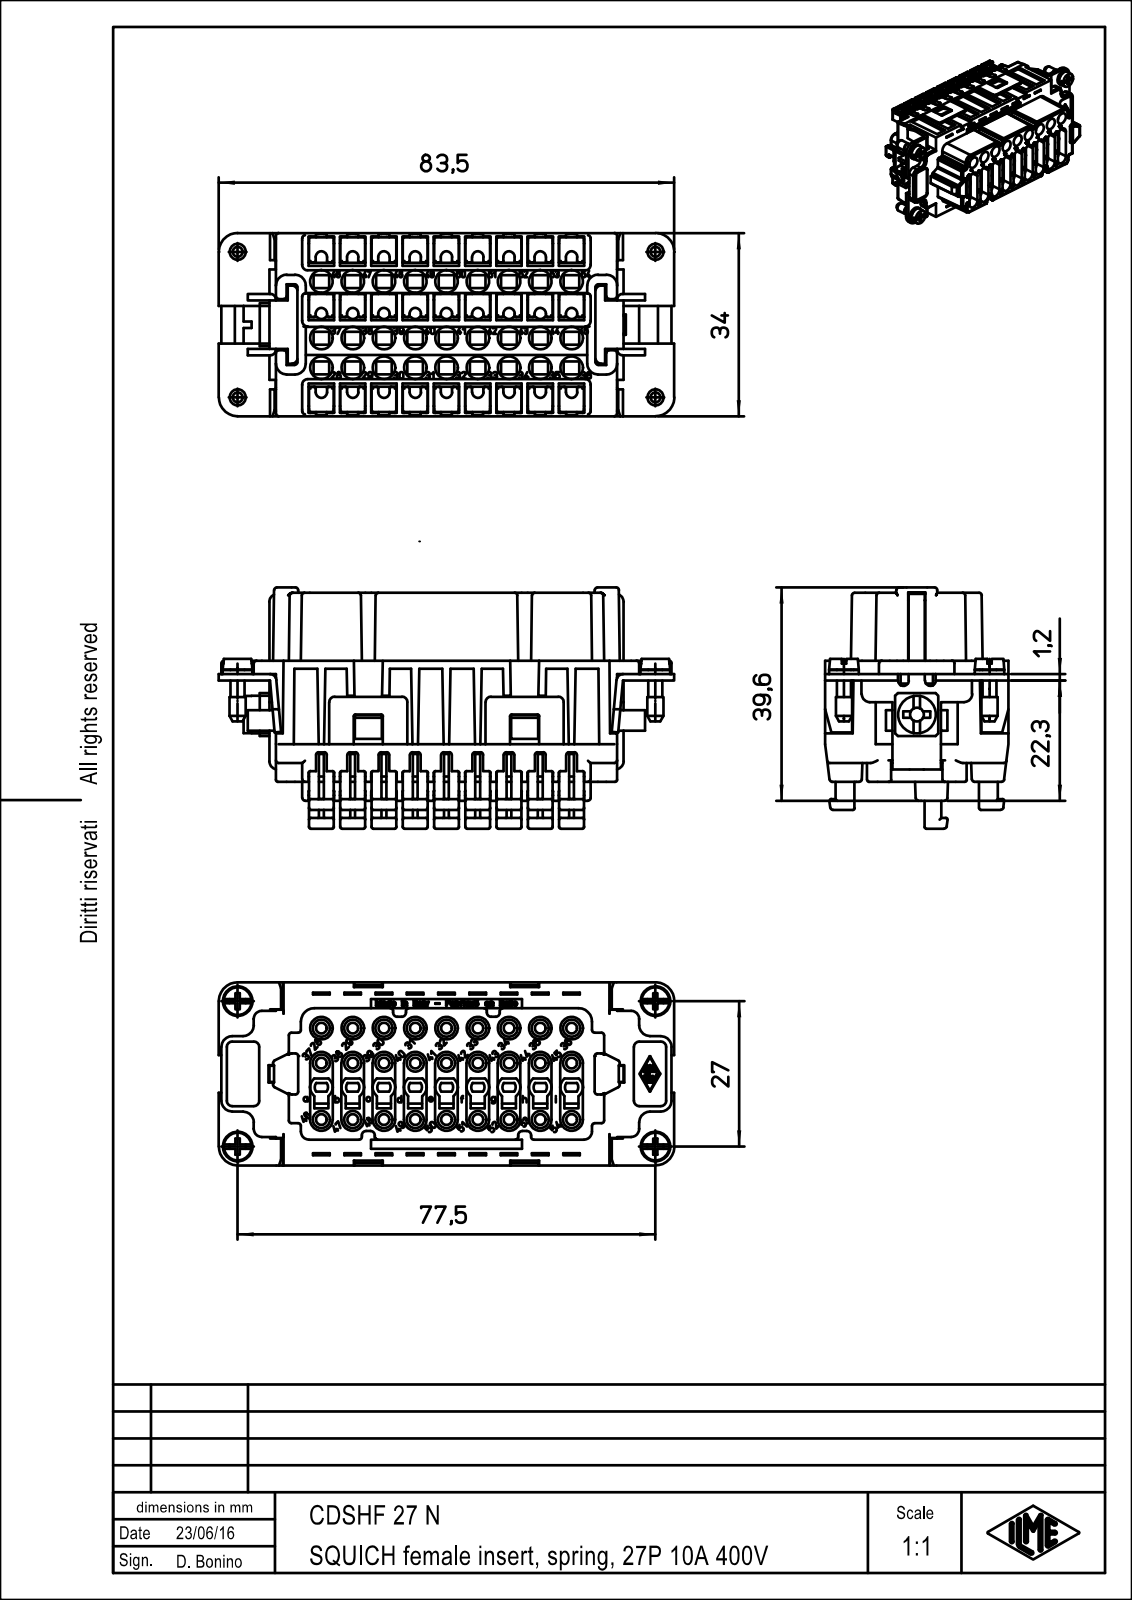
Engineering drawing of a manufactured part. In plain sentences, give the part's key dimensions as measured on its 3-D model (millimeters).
The part is named "CDSHF_27_N". Its 3-D file was written by "PTC Creo Elements/Direct Modeling 19.0B 21-Mar-2015 (C) Parametric Technology GmbH (AUTOMOTIVE_DESIGN)". It is 1 solid with 2232 faces: 1734 planar, 360 cylindrical and 138 other. Overall it measures 84.5 by 44.8 by 34 millimeters. Its volume is 60 353 cubic millimeters and its surface area 30 867 square millimeters. Round holes: 36 of diameter 4.2, 27 of diameter 2, 1 of diameter 4. Round bosses or shafts: 4 of diameter 5.5, 4 of diameter 3, 1 of diameter 7. Partial cylindrical surfaces (rounded edges, fillets, slot ends): 42 of radius 0.5, 27 of radius 1.05, 27 of radius 2.1, 22 of radius 1, 16 of radius 2, 12 of radius 1.5, 9 of radius 1.1, 9 of radius 1.25. The main face-to-face distances are 5.8, 1.2, 11.6, 7, 4.6, 17.4, 3.5, 23.2, 29, 0.9. The hole center spacings are 5.8, 29, 34.8, 5.82, 40.6, 11.6, 8.35, 17.49.
